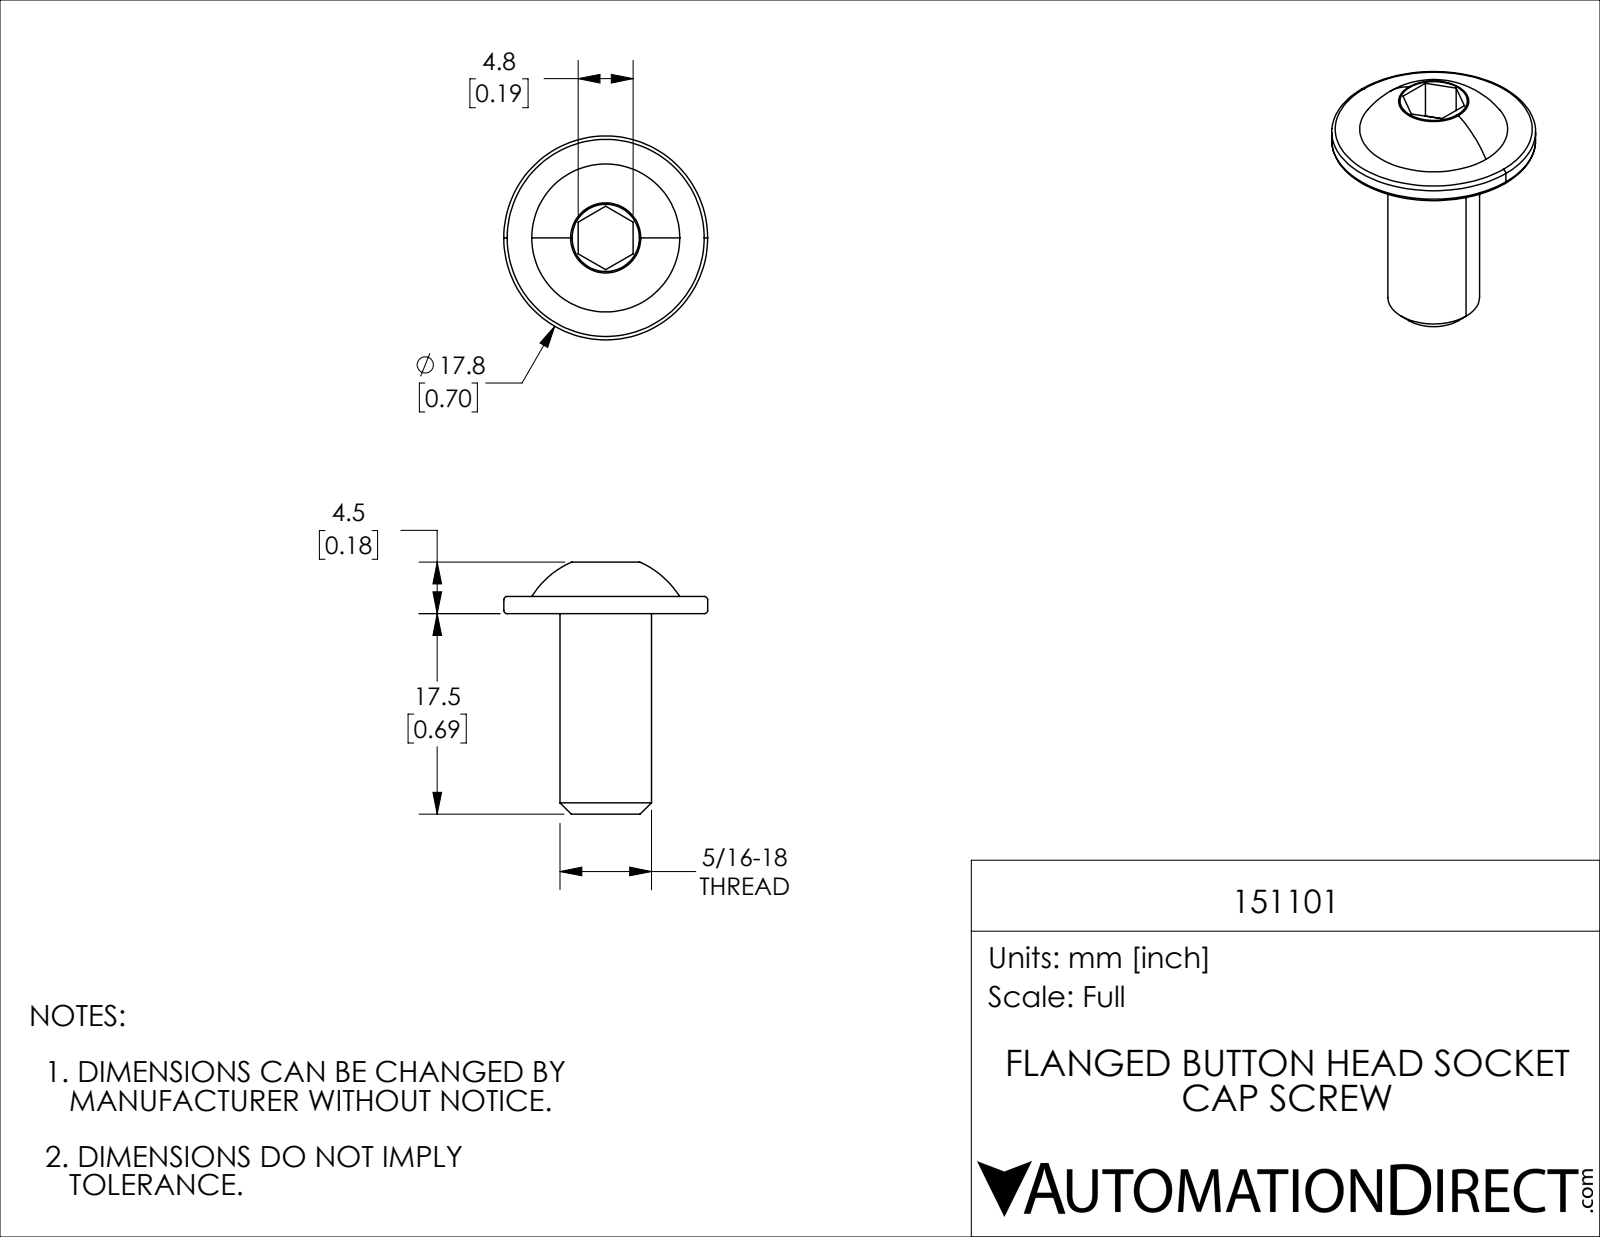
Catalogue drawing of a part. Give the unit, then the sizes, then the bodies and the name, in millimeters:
Units: millimetres
Overall size (bounding box): 22 × 17.8 × 17.8
Round bosses / shafts (diameter × count): ⌀17.8 ×1, ⌀8 ×1
Main face-to-face distances: 1.5, 4.8, 17.5, 19, 18.5, 1, 0.5, 22, 4.5, 3.5
Volume: 1 421 mm³ · Surface area: 1 089 mm²
Bodies: 1 solid, 25 faces (11 planar, 4 cylindrical, 10 other)
Part name (STEP PRODUCT): 151101
STEP written by: SolidWorks 2021 (CONFIG_CONTROL_DESIGN)
